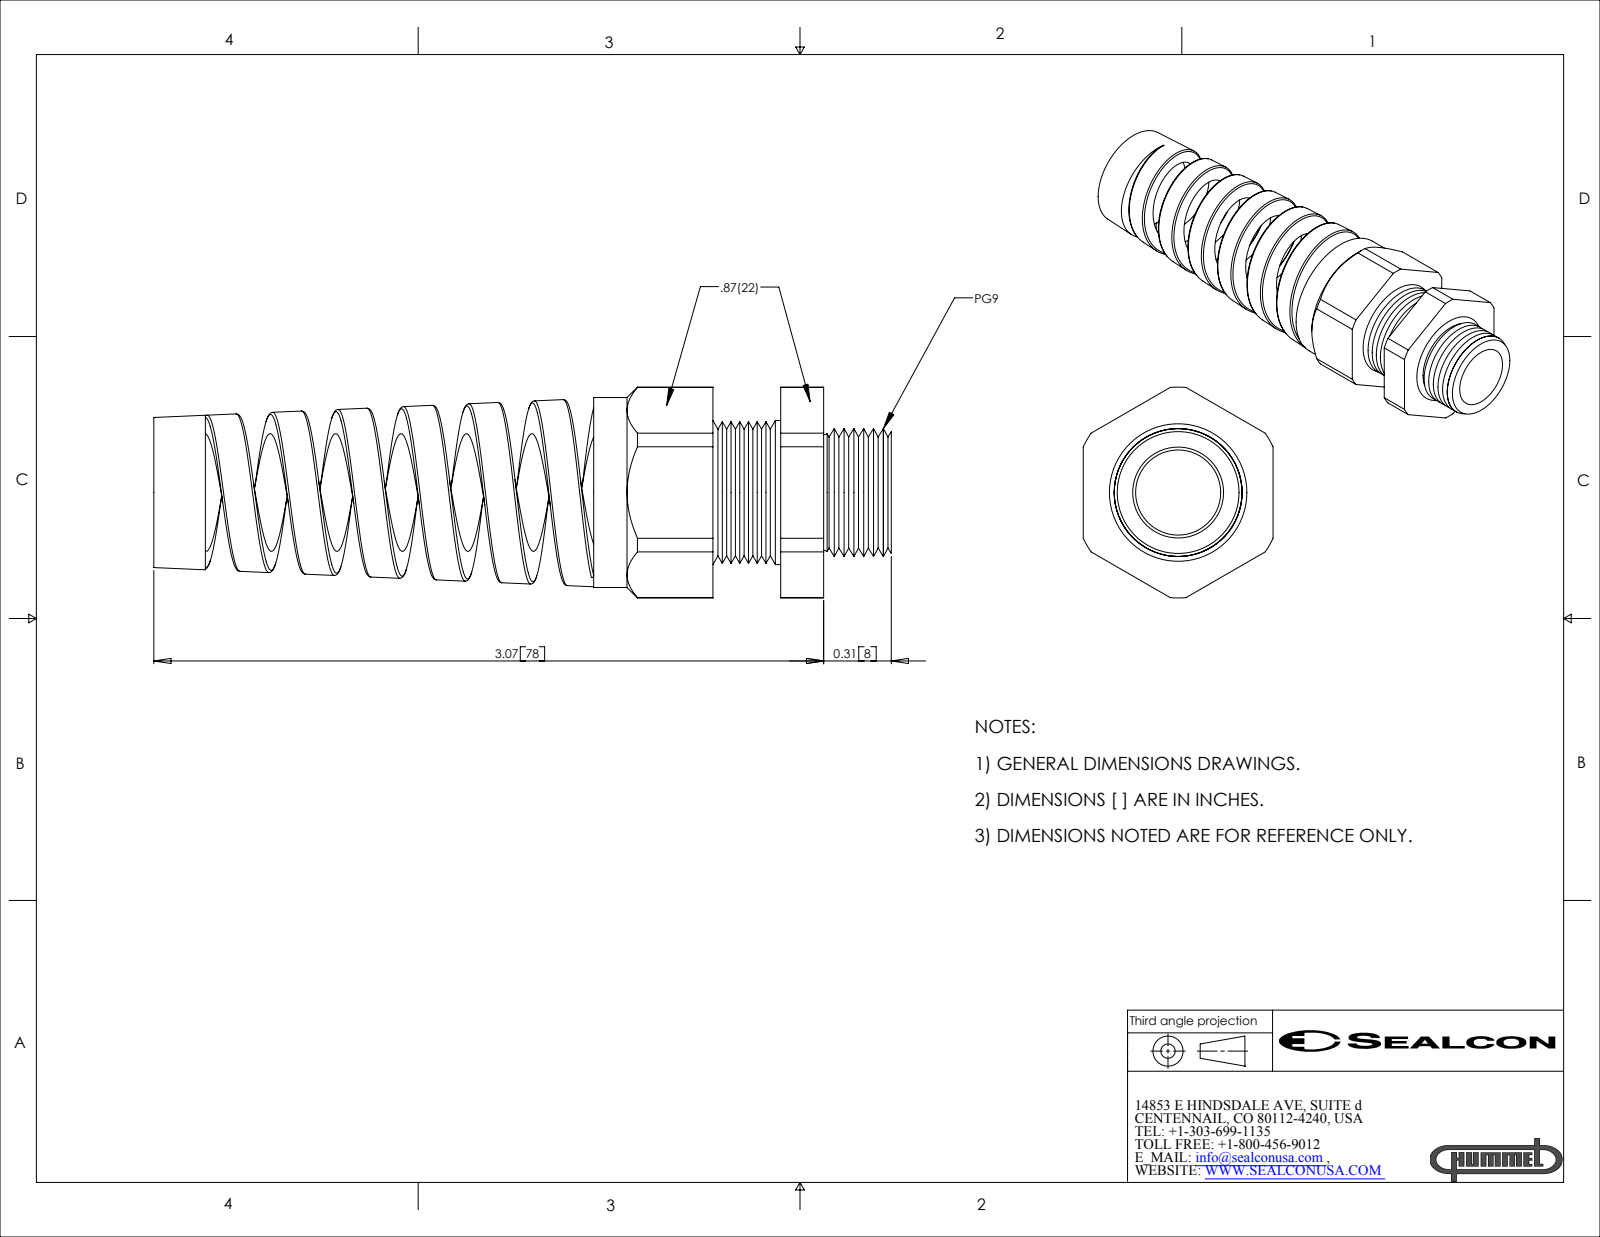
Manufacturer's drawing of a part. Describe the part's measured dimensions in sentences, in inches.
The part is named "CF09GA-GY". Its 3-D file was written by "SolidWorks 2007 (CONFIG_CONTROL_DESIGN)". It is 2 solids with 153 faces: 24 planar, 37 cylindrical and 92 other. Overall it measures 3.38 by 0.966 by 0.87 inches. Its volume is 0.73 cubic inches and its surface area 17.23 square inches. Round holes: 1 of diameter 0.39, 1 of diameter 0.54. Round bosses or shafts: 1 of diameter 0.87, 1 of diameter 0.66. Partial cylindrical surfaces (rounded edges, fillets, slot ends): 1 of radius 0.28, 1 of radius 0.483. The main face-to-face distances are 0.87, 0.508, 0.311, 0.197, 0.546, 0.857, 1.054, 2.016, 2.562, 2.873.
